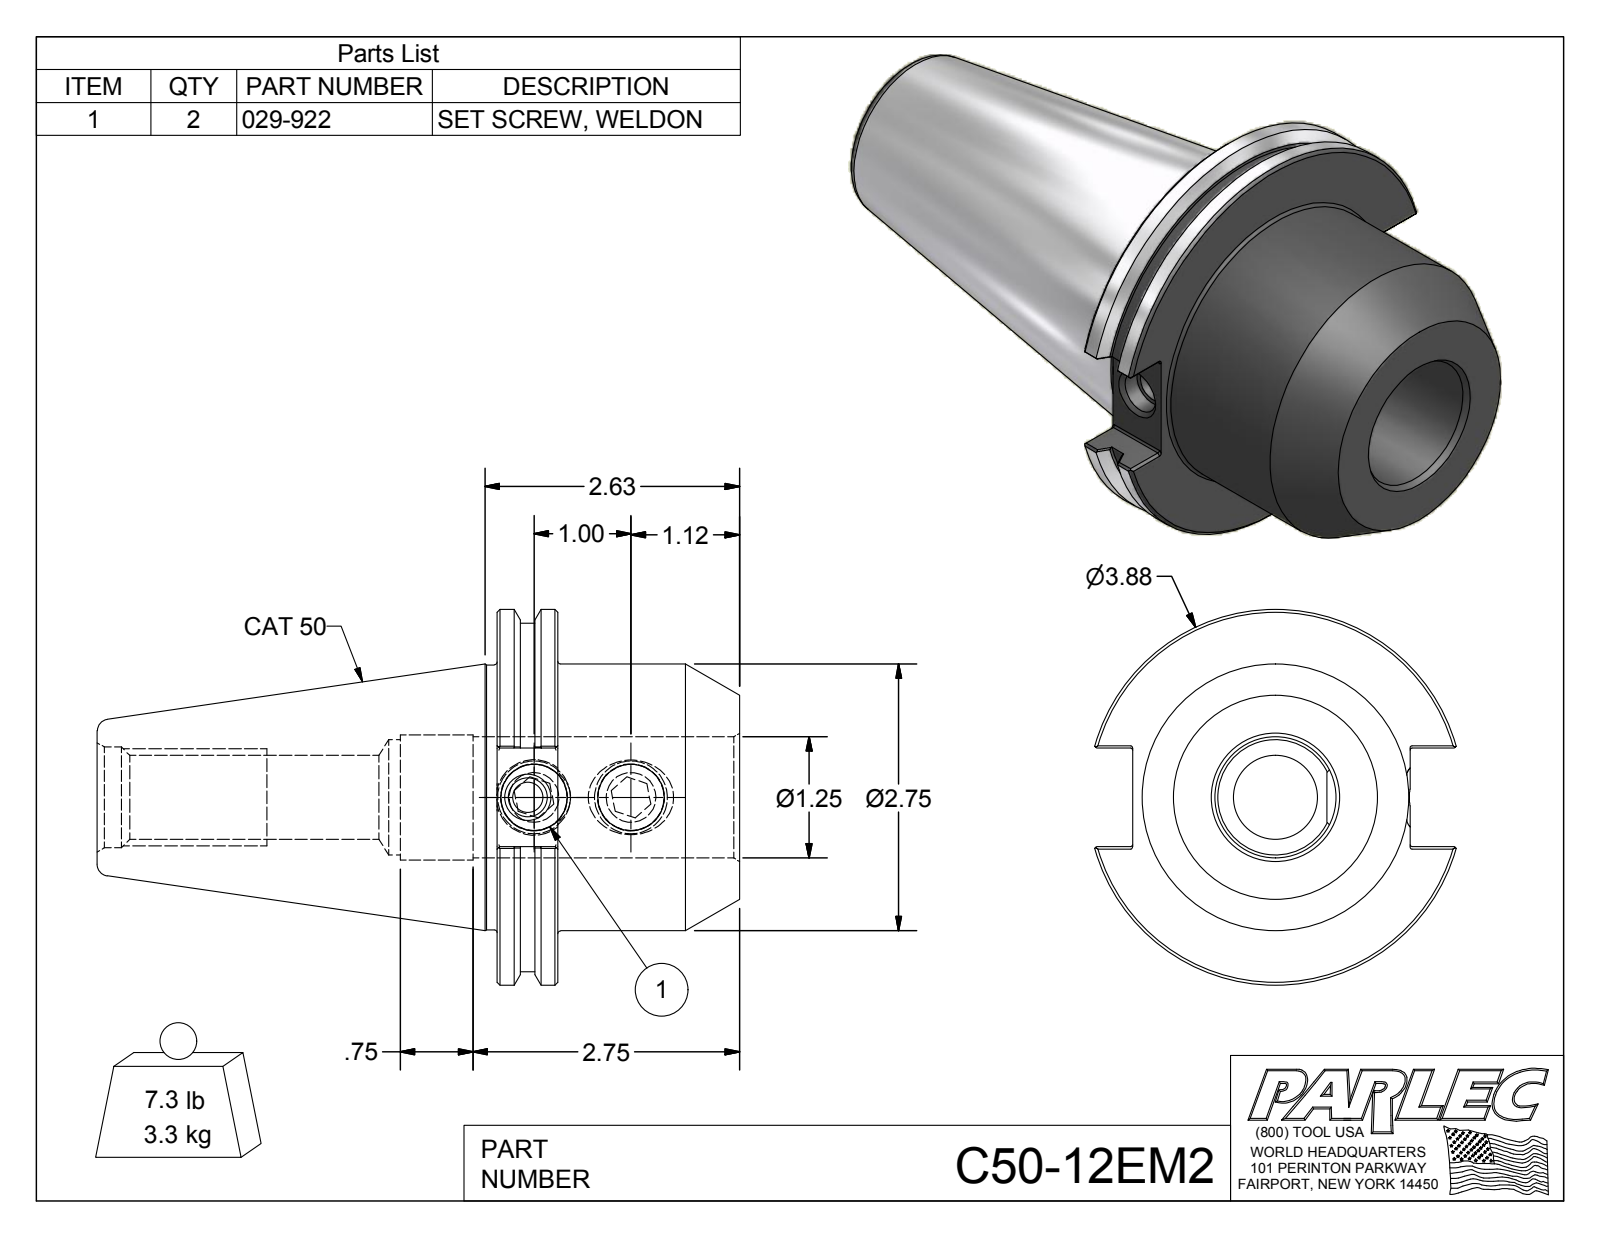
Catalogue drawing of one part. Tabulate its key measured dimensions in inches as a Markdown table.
| quantity | value |
| --- | --- |
| part name | C50-12EM2; C50-12EM2-1; 029-922 |
| STEP written by | Autodesk Inventor 2012 (AUTOMOTIVE_DESIGN) |
| units | inches |
| bodies | 3 solids, 117 faces (52 planar, 31 cylindrical, 34 other) |
| overall size | 6.625 × 3.875 × 3.729 |
| volume | 26.15 in³ |
| surface area | 98.16 in² |
| round holes (diameter × count) | 0.682 × 2, 0.315 × 1, 0.399 × 1, 0.865 × 1, 1.038 × 1, 1.19 × 1, 1.25 × 1, 1.29 × 1 |
| round bosses / shafts (diameter × count) | 0.75 × 2, 3.875 × 1, 3.594 × 1, 2.75 × 1, 2.73 × 1 |
| partial cylindrical surfaces (radius × count) | 0.02 × 12 |
| main face-to-face distances | 0.625, 2.5, 1.875, 0.375, 4.125, 4.75, 6.625, 2.628, 0.625, 2.003 |
| hole center spacings | 0.065, 1, 1.065 |
